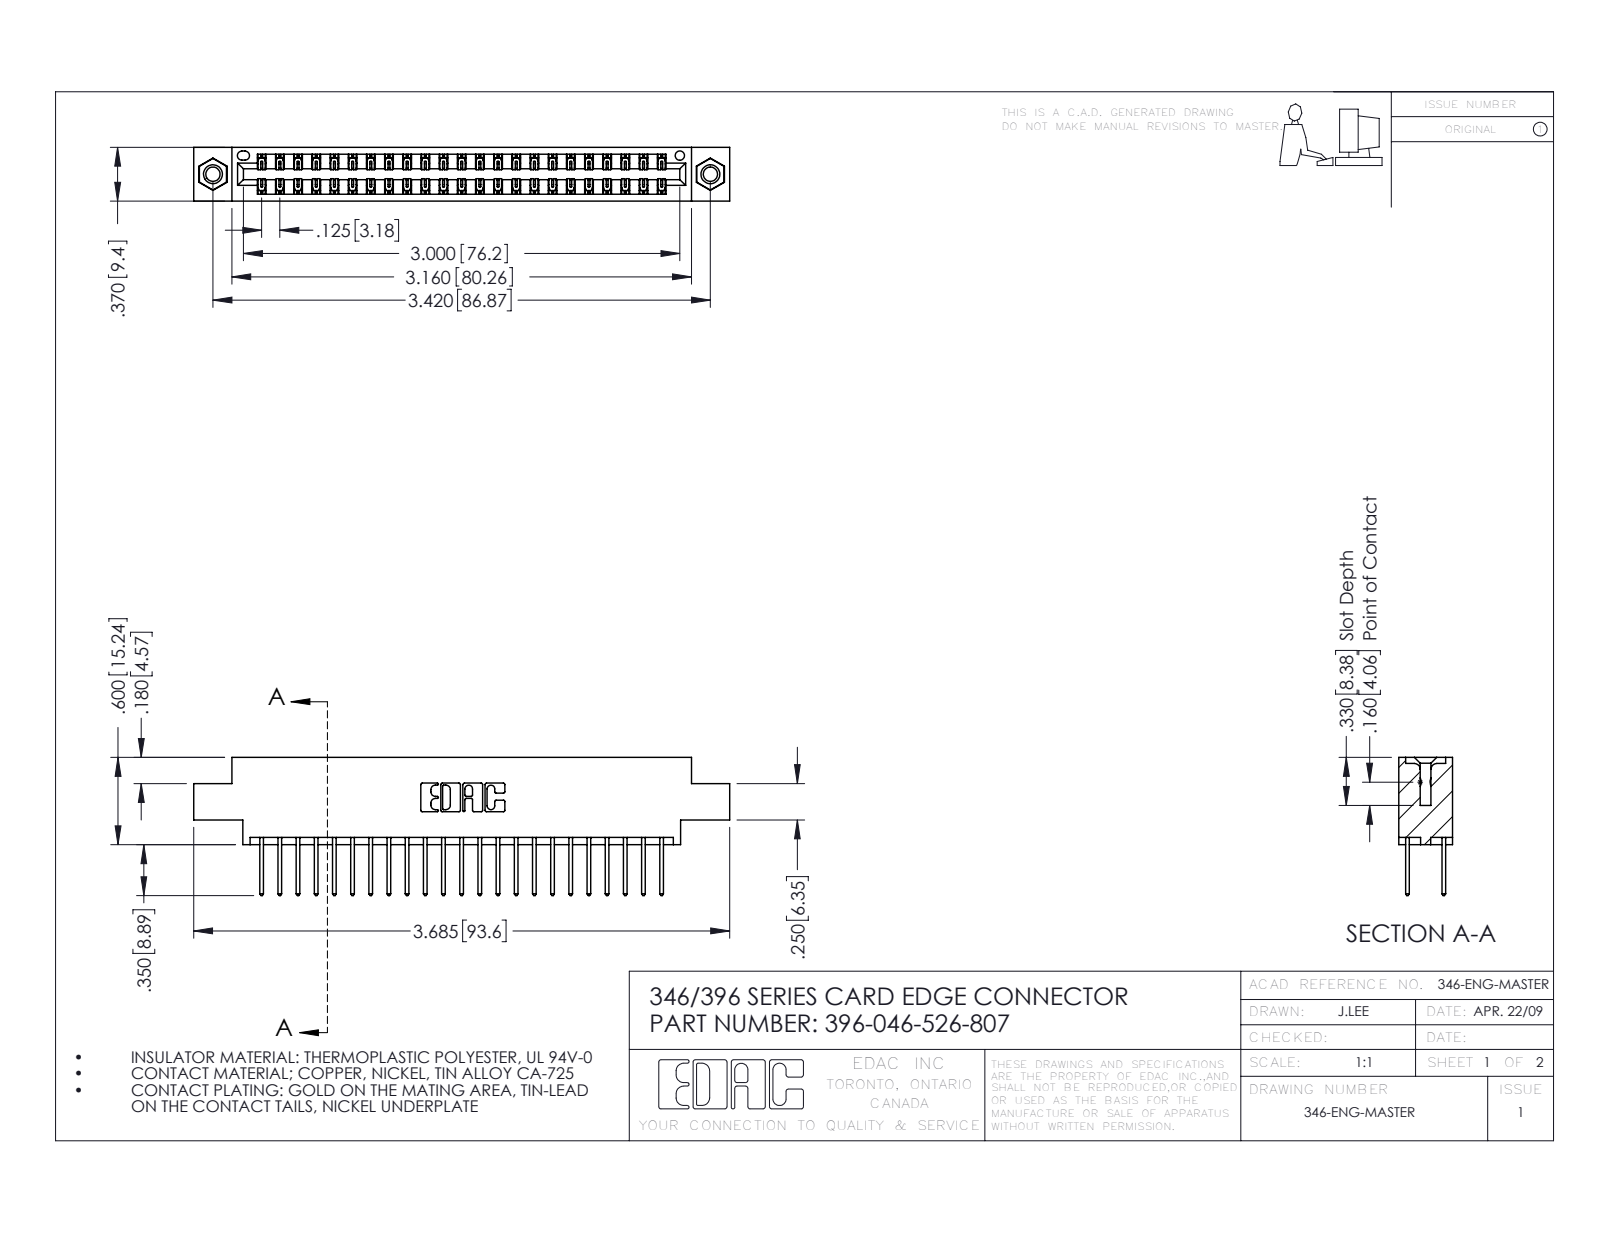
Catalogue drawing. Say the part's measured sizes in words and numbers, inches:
The part is named "396-046-526-807; 345-292-001_345-293-126; 345-250-001_345-250-005-103; 346 Part_0.170 Offset - 0.156 Dia-TI". Its 3-D file was written by "SolidWorks 2016 (CONFIG_CONTROL_DESIGN)". It is 49 solids with 2578 faces: 1722 planar, 840 cylindrical and 16 other. Overall it measures 3.685 by 0.95 by 0.37 inches. Its volume is 0.542 cubic inches and its surface area 19.33 square inches. Round holes: 2 of diameter 0.098, 2 of diameter 0.125, 2 of diameter 0.156, 1 of diameter 0.064. Round bosses or shafts: 2 of diameter 0.155. Partial cylindrical surfaces (rounded edges, fillets, slot ends): 69 of radius 0.006, 46 of radius 0.01, 22 of radius 0.01, 6 of radius 0.007, 6 of radius 0.031, 3 of radius 0.026, 2 of radius 0.014, 2 of radius 0.022. The main face-to-face distances are 0.048, 0.322, 0.25, 0.37, 0.072, 0.298, 0.025, 0.275, 0.222, 0.148. The hole center spacings are 0.246, 3.212, 3.42.
